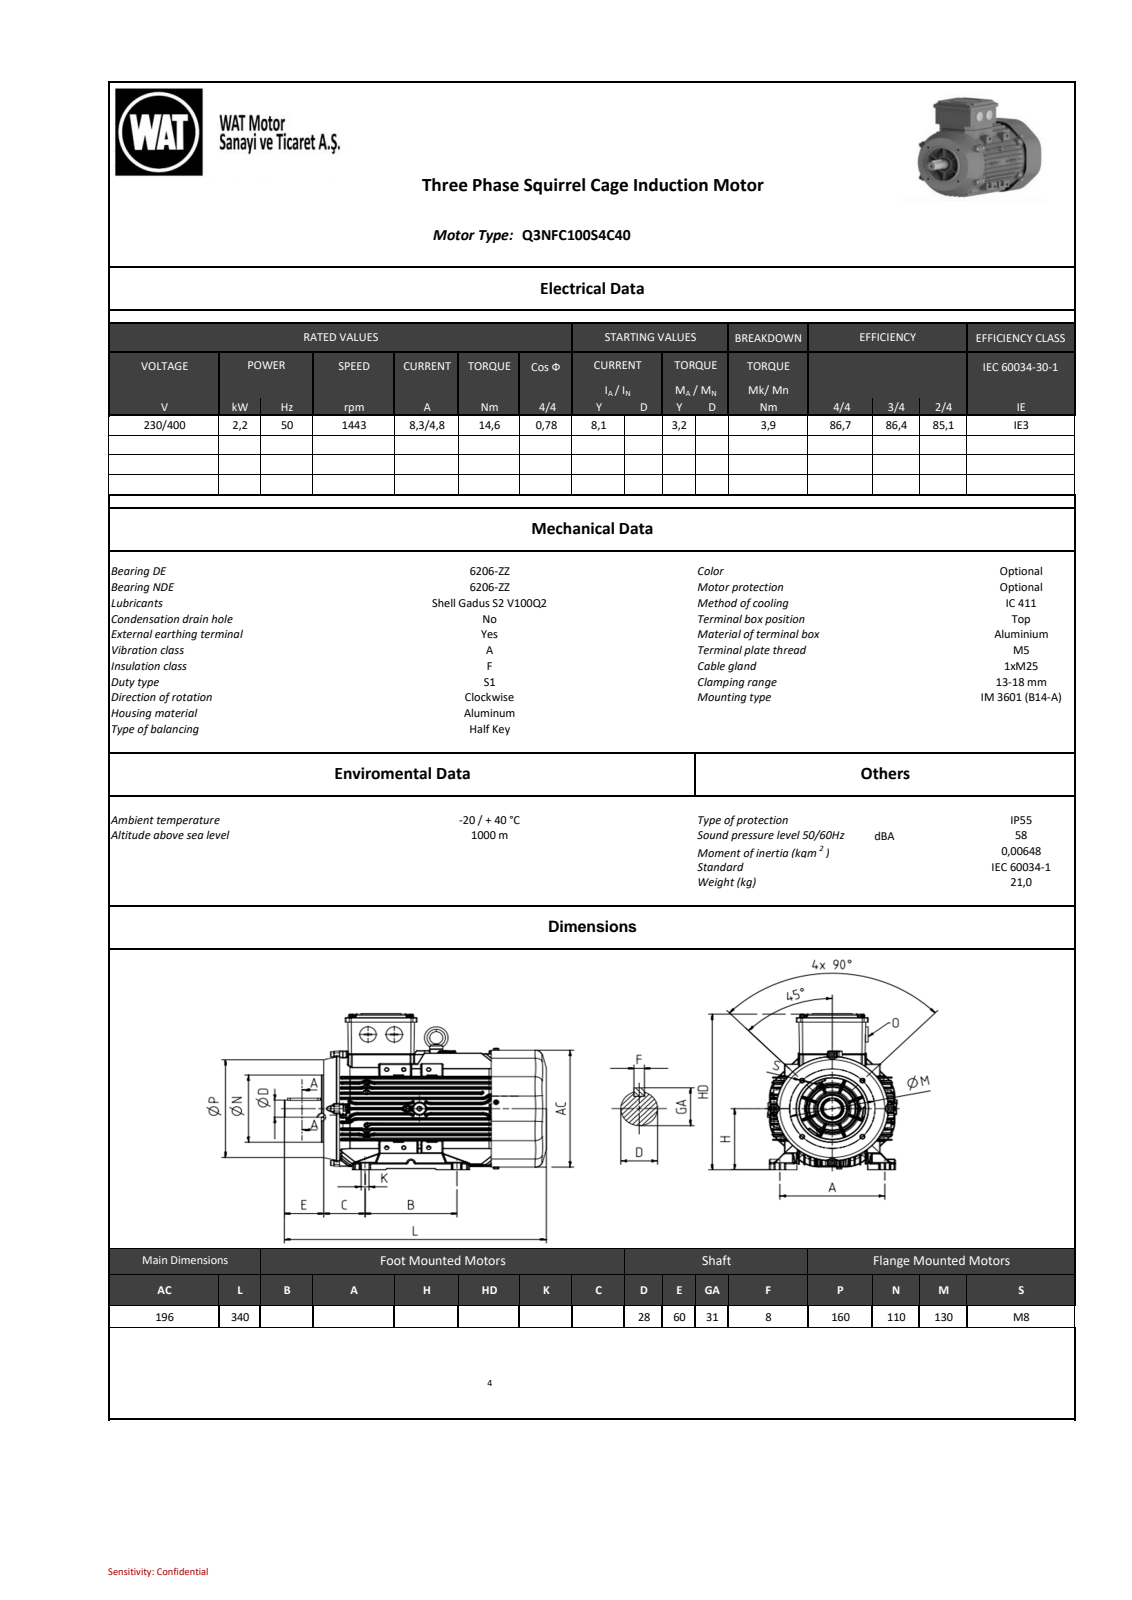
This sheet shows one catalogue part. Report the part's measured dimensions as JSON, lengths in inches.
{"part_name": "C90127E0127Fj929", "step_written_by": "SIEMENS PLM Software NX 11.0 (AUTOMOTIVE_DESIGN)", "units": "inches", "bodies": {"solids": 0, "faces": 13385, "planar": 2782, "cylindrical": 4182, "other": 6421}, "overall_size": [13.386, 9.016, 7.874], "round_holes": [[0.197, 6], [0.256, 6], [0.268, 4], [0.079, 2], [0.098, 2], [0.118, 2], [0.472, 2], [0.157, 1], [0.335, 1], [0.413, 1], [1.126, 1], [1.297, 1]], "round_bosses_or_shafts": [[0.315, 7], [0.157, 7], [0.465, 6], [0.394, 6], [0.236, 6], [1.378, 2], [1.094, 2], [0.994, 2]], "partial_cylinders_radius": [[0.02, 1221], [0.03, 586], [0.031, 480], [0.039, 263], [0.01, 144], [0.059, 130], [0.157, 99], [0.118, 42]], "face_to_face_distances": [0.031, 0.079, 1.614, 0.551, 9.409, 1.583, 11.024, 10.992, 1.102, 0.208], "hole_center_spacings": [3.622, 1.427, 2.559, 2.561, 3.619, 3.733, 3.785, 5.039]}
